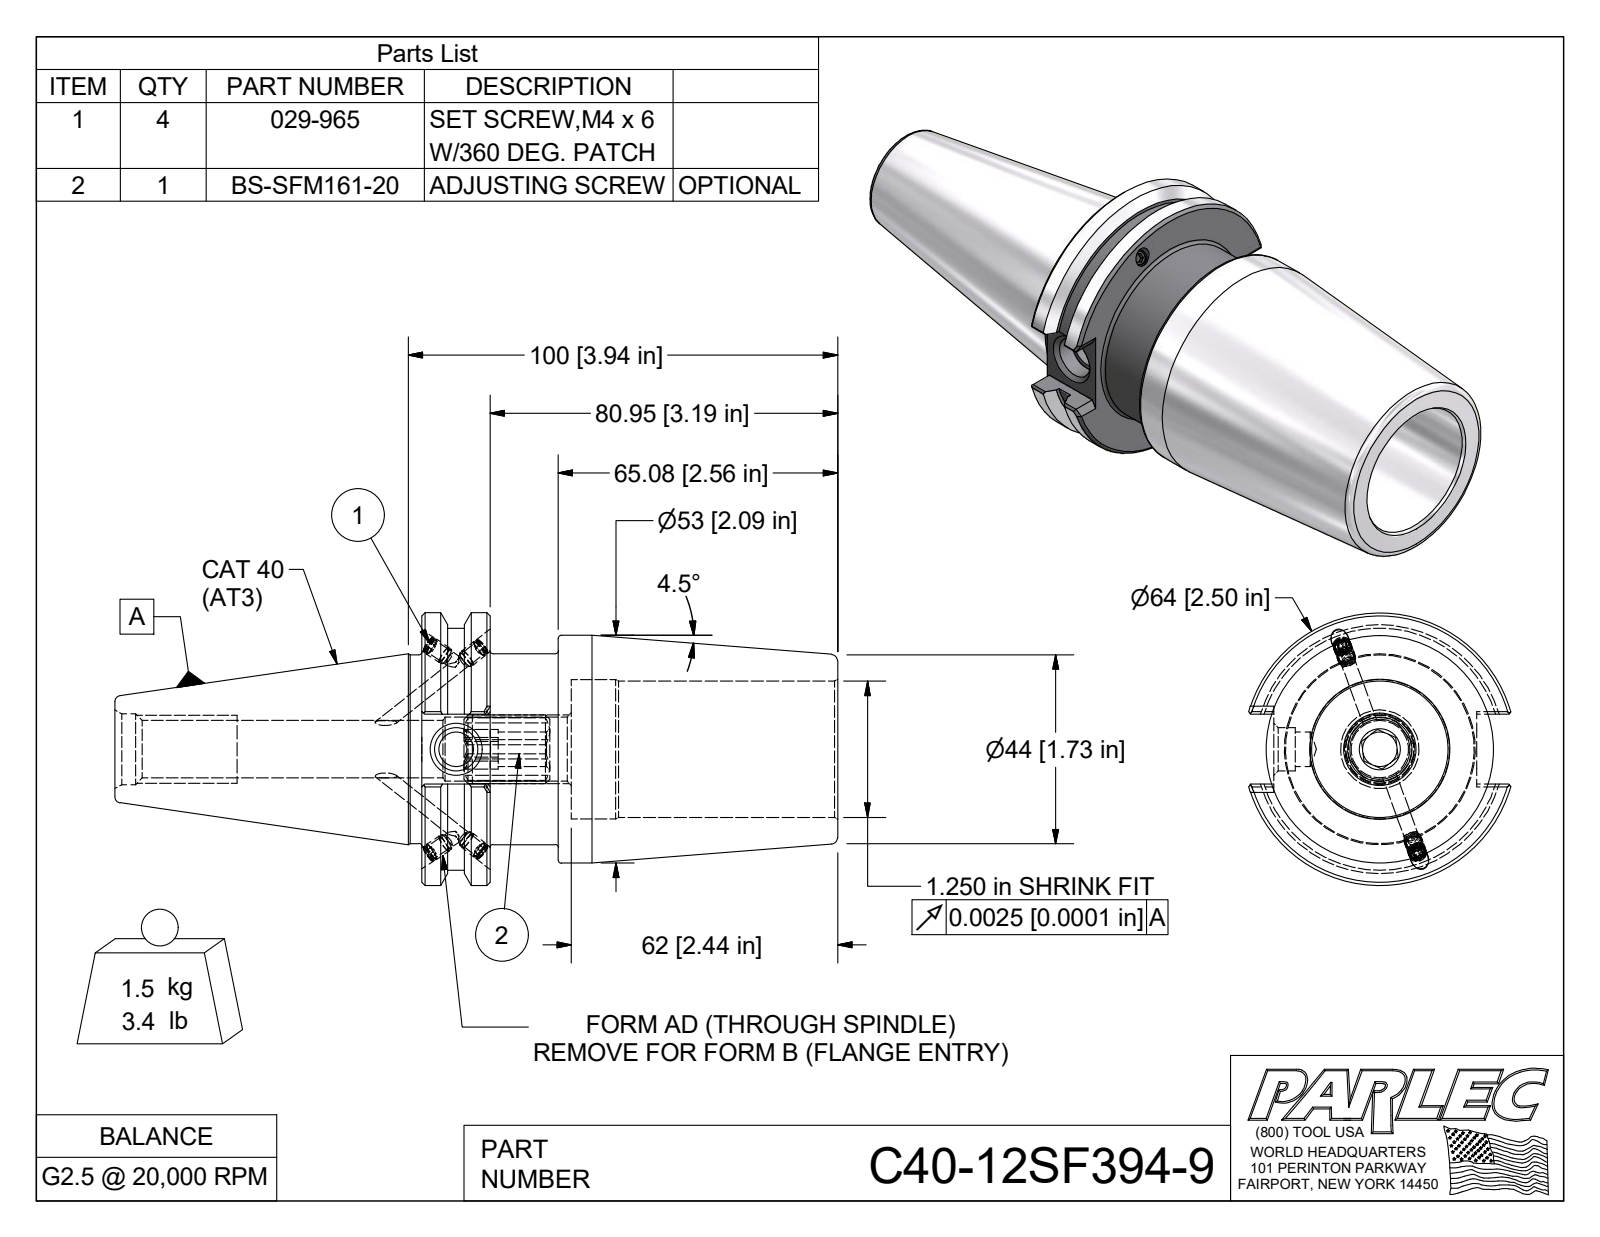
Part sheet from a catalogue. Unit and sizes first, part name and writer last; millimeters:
Units: millimetres
Overall size (bounding box): 168.3 × 63.5 × 61
Round holes (diameter × count): ⌀3.3 ×4, ⌀4.1 ×4, ⌀31.7 ×1, ⌀32.5 ×1
Round bosses / shafts (diameter × count): ⌀4.2 ×4, ⌀4 ×4, ⌀63.5 ×1, ⌀56.4 ×1, ⌀53 ×1, ⌀44.5 ×1, ⌀43.9 ×1
Partial cylindrical surfaces — rounded edges, fillets, slot ends (radius × count): R8 ×1
Main face-to-face distances: 15.9, 34.8, 18.9, 96.8, 80.9, 62, 31.8, 3.1, 65.1, 16.3
Volume: 197 500 mm³ · Surface area: 42 920 mm²
Bodies: 6 solids, 176 faces (88 planar, 33 cylindrical, 55 other)
Part name (STEP PRODUCT): C40-12SF394-9; C40BC-12SF394-9-1; 029-965; BS-SFM161-20
STEP written by: Autodesk Inventor 2009 (AUTOMOTIVE_DESIGN)
